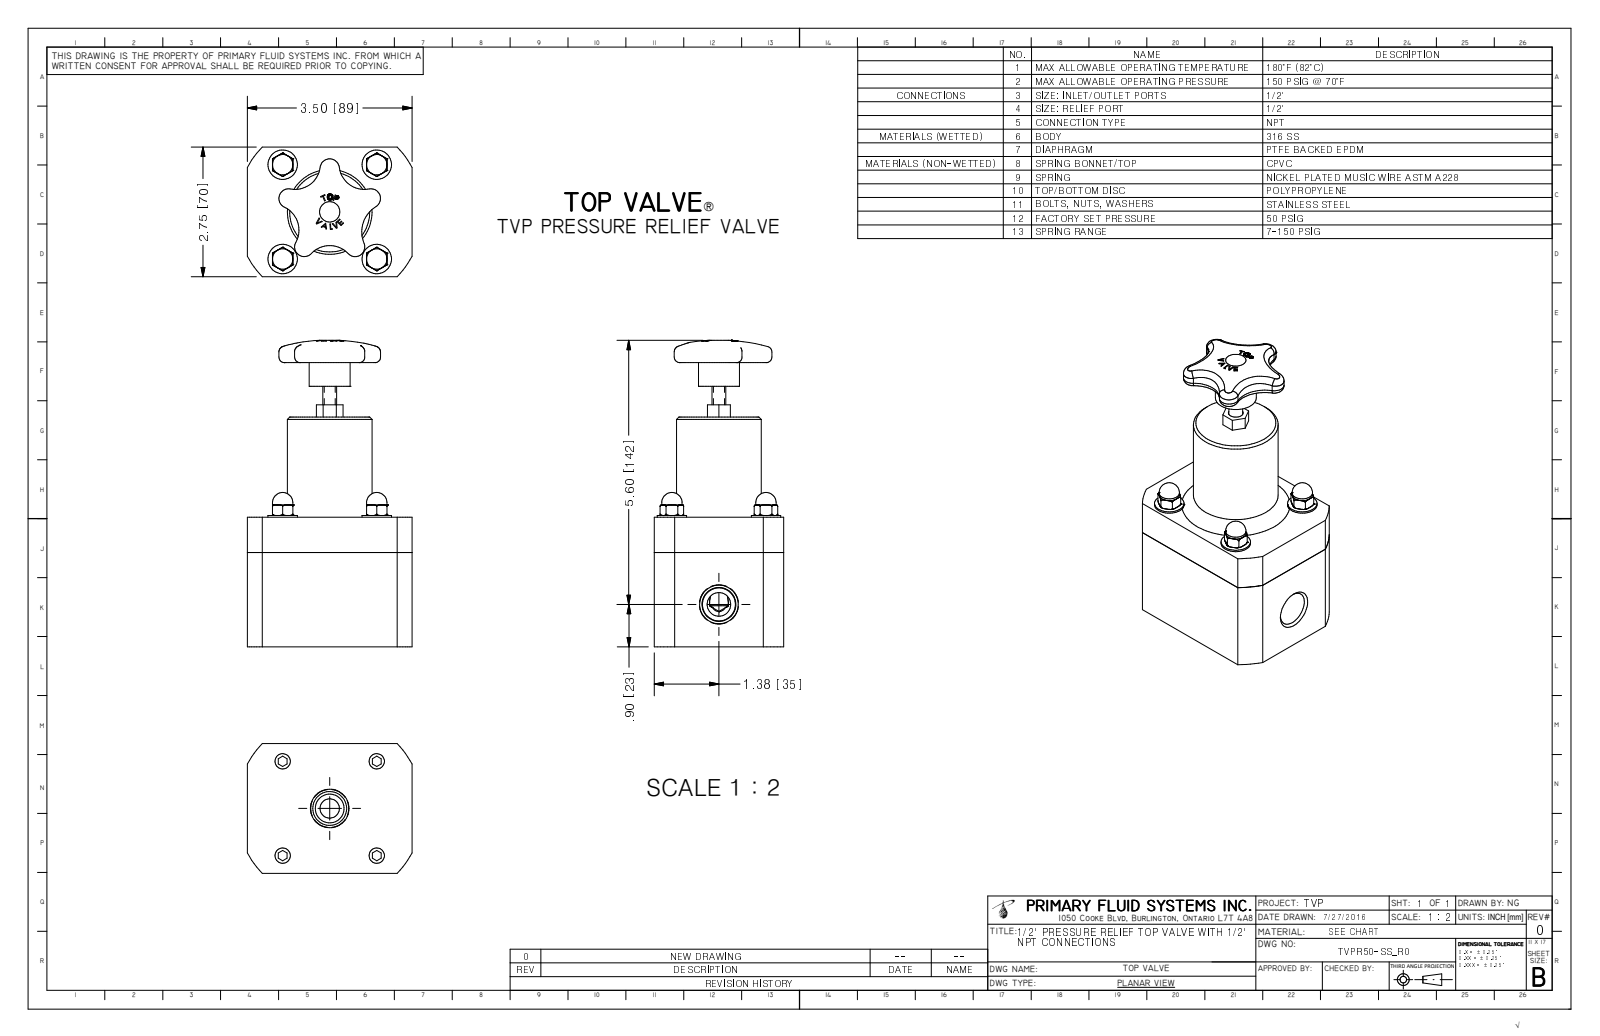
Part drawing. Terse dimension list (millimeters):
name: TVPR50-SS_R0
written by: Autodesk Inventor 2009 (AUTOMOTIVE_DESIGN)
unit: mm
bodies: 1 solid, 316 faces (123 planar, 44 cylindrical, 149 other)
size: 165.1 × 88.9 × 69.9
volume: 523 400 mm³; area: 52 660 mm²
holes: 4× ⌀4.4, 2× ⌀18.3, 1× ⌀61
bosses: 4× ⌀15.9, 4× ⌀11, 1× ⌀60.3, 1× ⌀45.7, 1× ⌀22.1, 1× ⌀7.4
rounds: 5× R2.2, 5× R5.2, 4× R13.6, 4× R16.7, 1× R15.9, 1× R18.9, 1× R50.5
face distances: 69.9, 88.9, 69.9, 123.8, 54, 17.8, 71.1, 11, 70.8, 0.9
hole spacings: 35.9, 50.8, 71.8
